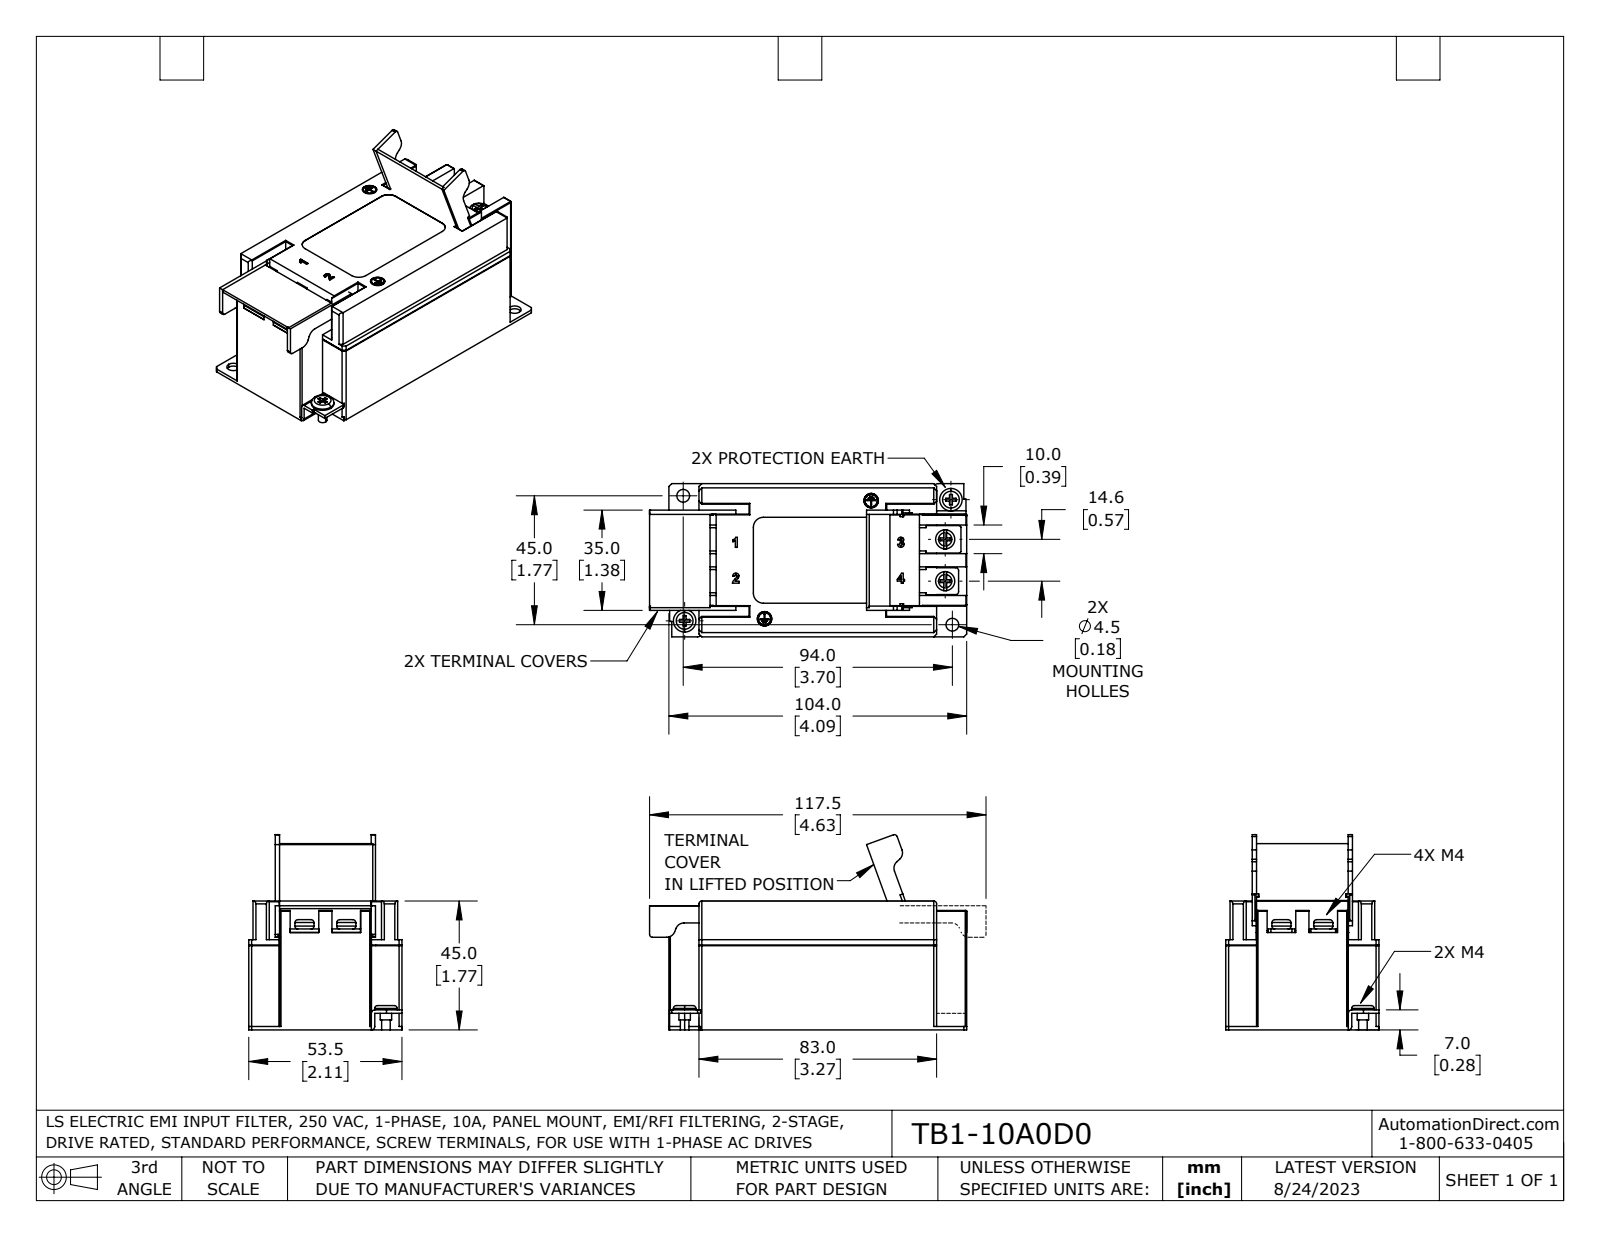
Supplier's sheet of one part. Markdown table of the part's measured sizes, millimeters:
| quantity | value |
| --- | --- |
| part name | TB1-10A0D0 |
| STEP written by | SolidWorks 2021 (AUTOMOTIVE_DESIGN) |
| units | millimeters |
| bodies | 12 solids, 635 faces (463 planar, 113 cylindrical, 59 other) |
| overall size | 117.5 × 53.5 × 45 |
| volume | 207 863 mm³ |
| surface area | 39 686 mm² |
| round holes (diameter × count) | 2 × 2, 4.5 × 2, 5 × 2 |
| round bosses / shafts (diameter × count) | 6.68 × 4, 7.85 × 2, 4.4 × 2, 3.99 × 2, 3.5 × 2, 3 × 2, 1.37 × 2 |
| partial cylindrical surfaces (radius × count) | 0.25 × 10, 1 × 6, 0.5 × 4, 1.2 × 4, 3 × 4, 3.5 × 4, 1.5 × 2, 0.74 × 1 |
| main face-to-face distances | 42.75, 10.75, 53.5, 45, 9.25, 1.5, 1.65, 32, 10.65, 42.85 |
| hole center spacings | 10, 20.53, 22.96, 28.96, 31.13, 51.47, 51.77, 52.58 |
